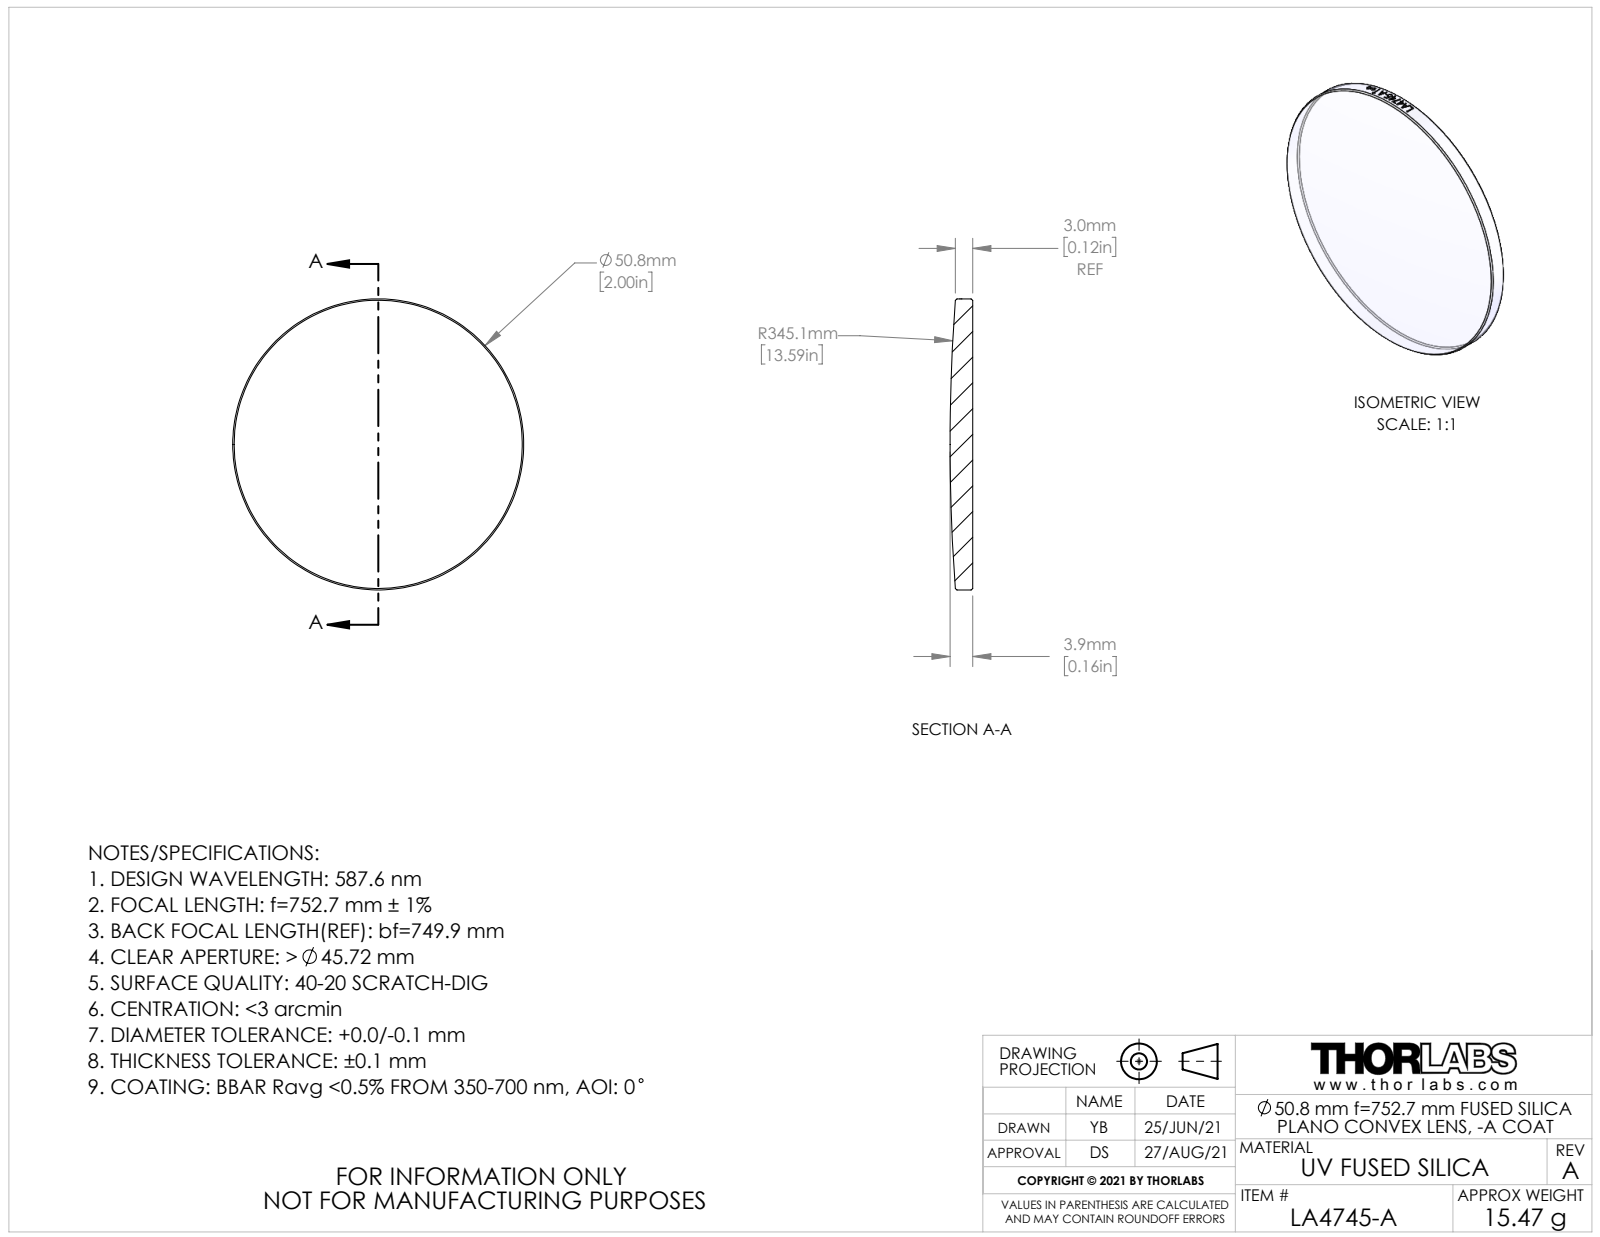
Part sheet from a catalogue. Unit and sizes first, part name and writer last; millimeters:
Units: millimetres
Overall size (bounding box): 50.8 × 50.8 × 3.94
Round bosses / shafts (diameter × count): ⌀50.8 ×1
Volume: 7 022 mm³ · Surface area: 4 490 mm²
Bodies: 1 solid, 25 faces (1 planar, 18 cylindrical, 6 other)
Part name (STEP PRODUCT): CTN017543-E0W; CTN017571
STEP written by: SolidWorks 2018 (AUTOMOTIVE_DESIGN)
